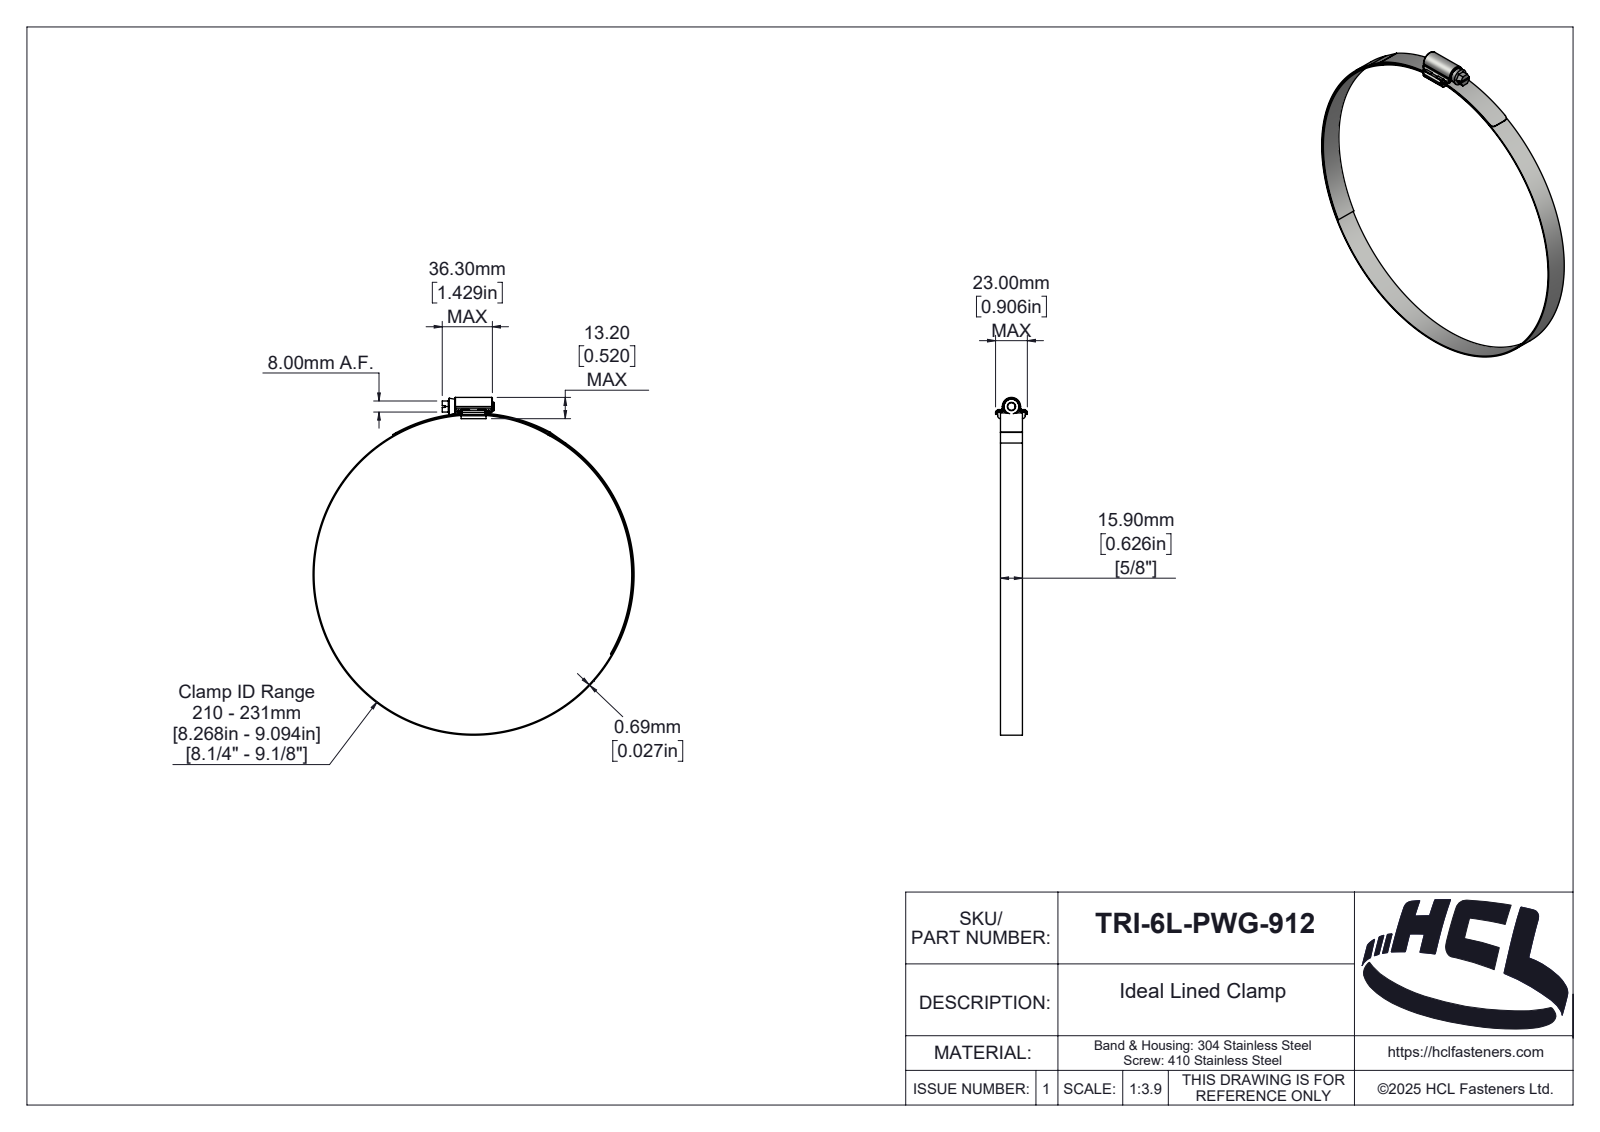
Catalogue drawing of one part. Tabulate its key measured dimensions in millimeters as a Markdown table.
| quantity | value |
| --- | --- |
| part name | TRI-6L-PWG-912 |
| STEP written by | SolidWorks 2025 (AUTOMOTIVE_DESIGN) |
| units | millimeters |
| bodies | 4 solids, 268 faces (87 planar, 102 cylindrical, 79 other) |
| overall size | 244.39 × 232.38 × 23 |
| volume | 16 495 mm³ |
| surface area | 38 785 mm² |
| round holes (diameter × count) | 231 × 1 |
| round bosses / shafts (diameter × count) | 232.38 × 1, 10.7 × 1, 6 × 1 |
| partial cylindrical surfaces (radius × count) | 1 × 14, 0.5 × 4, 1.5 × 4, 2 × 3, 0.1 × 2, 2.1 × 2, 3 × 2, 0.46 × 1 |
| main face-to-face distances | 15.9, 2, 0.69, 17.9, 4.9, 1.2, 4.55, 3.35, 15.35, 2.55 |
